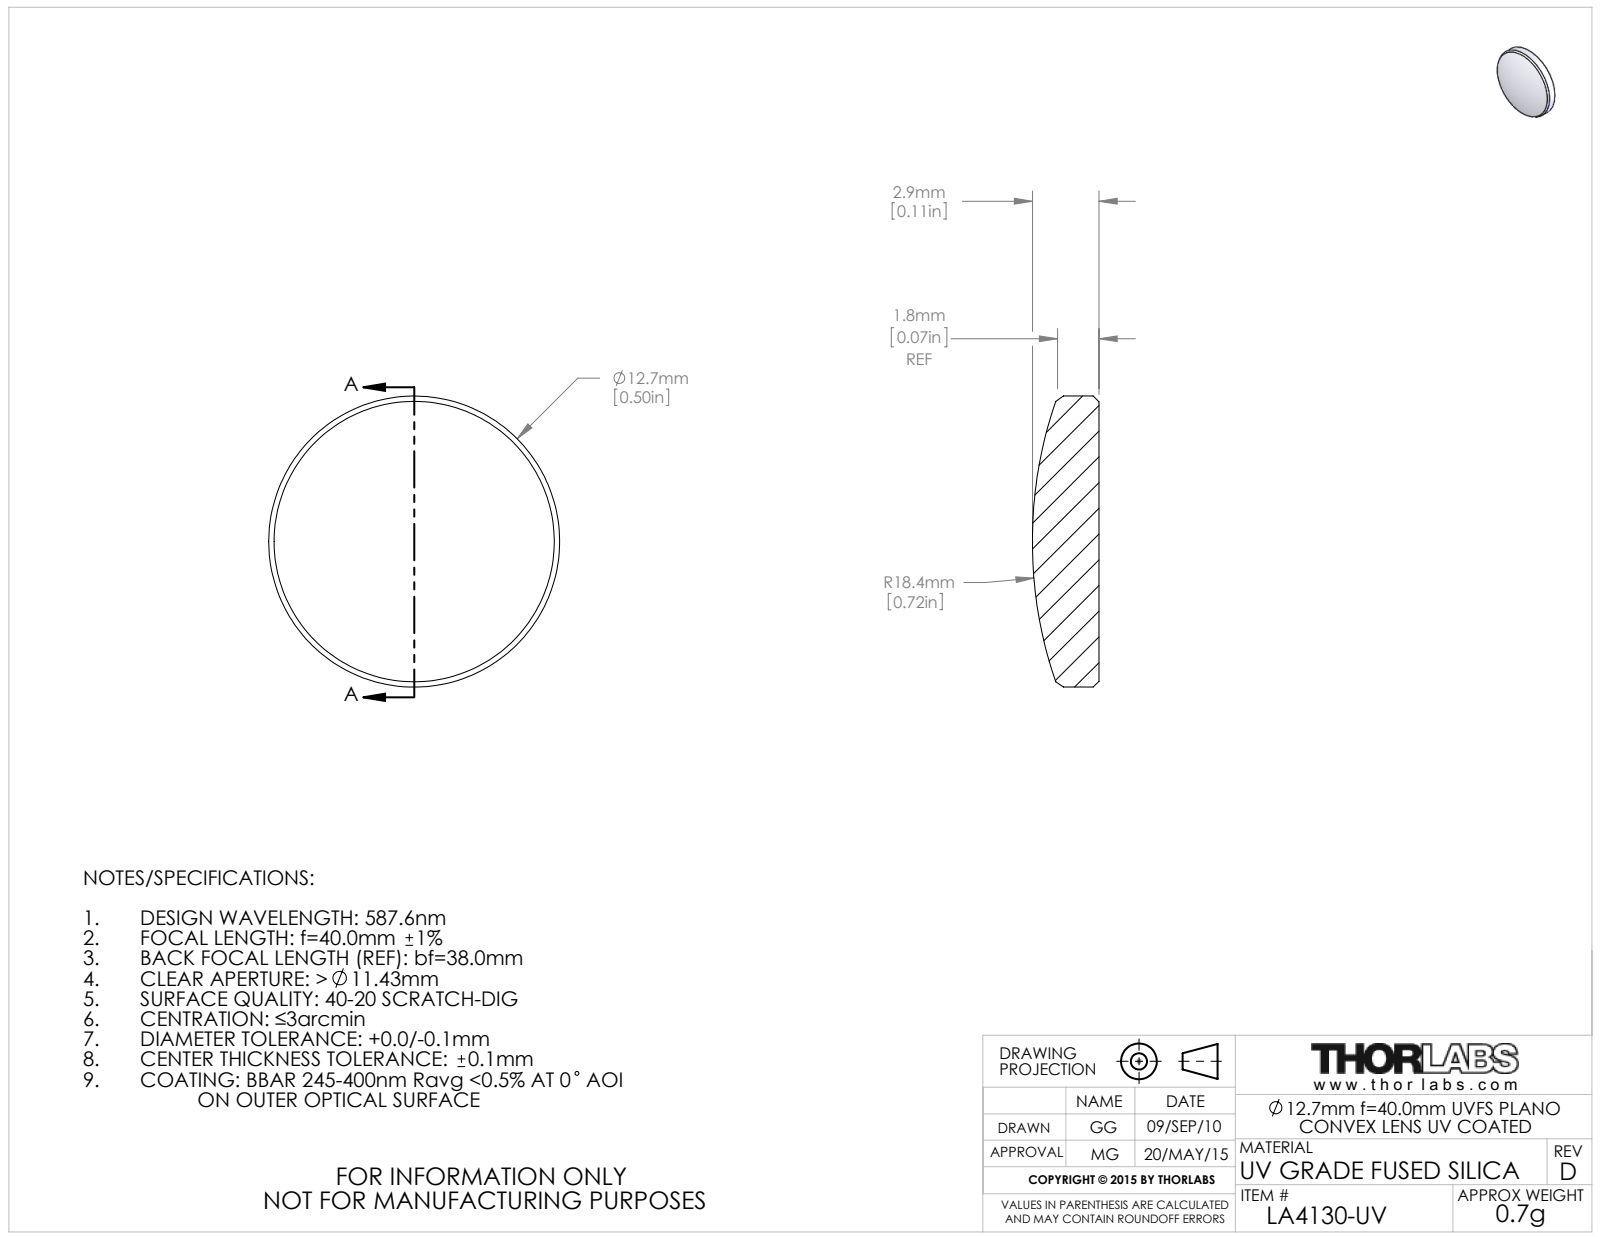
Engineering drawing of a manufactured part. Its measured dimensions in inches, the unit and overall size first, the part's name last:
Units: inches
Overall size (bounding box): 0.5 × 0.5 × 0.114
Round bosses / shafts (diameter × count): ⌀0.5 ×1
Volume: 0.018 in³ · Surface area: 0.494 in²
Bodies: 1 solid, 9 faces (1 planar, 2 cylindrical, 6 other)
Part name (STEP PRODUCT): 4274-E0W
STEP written by: SolidWorks 2014 (CONFIG_CONTROL_DESIGN)
